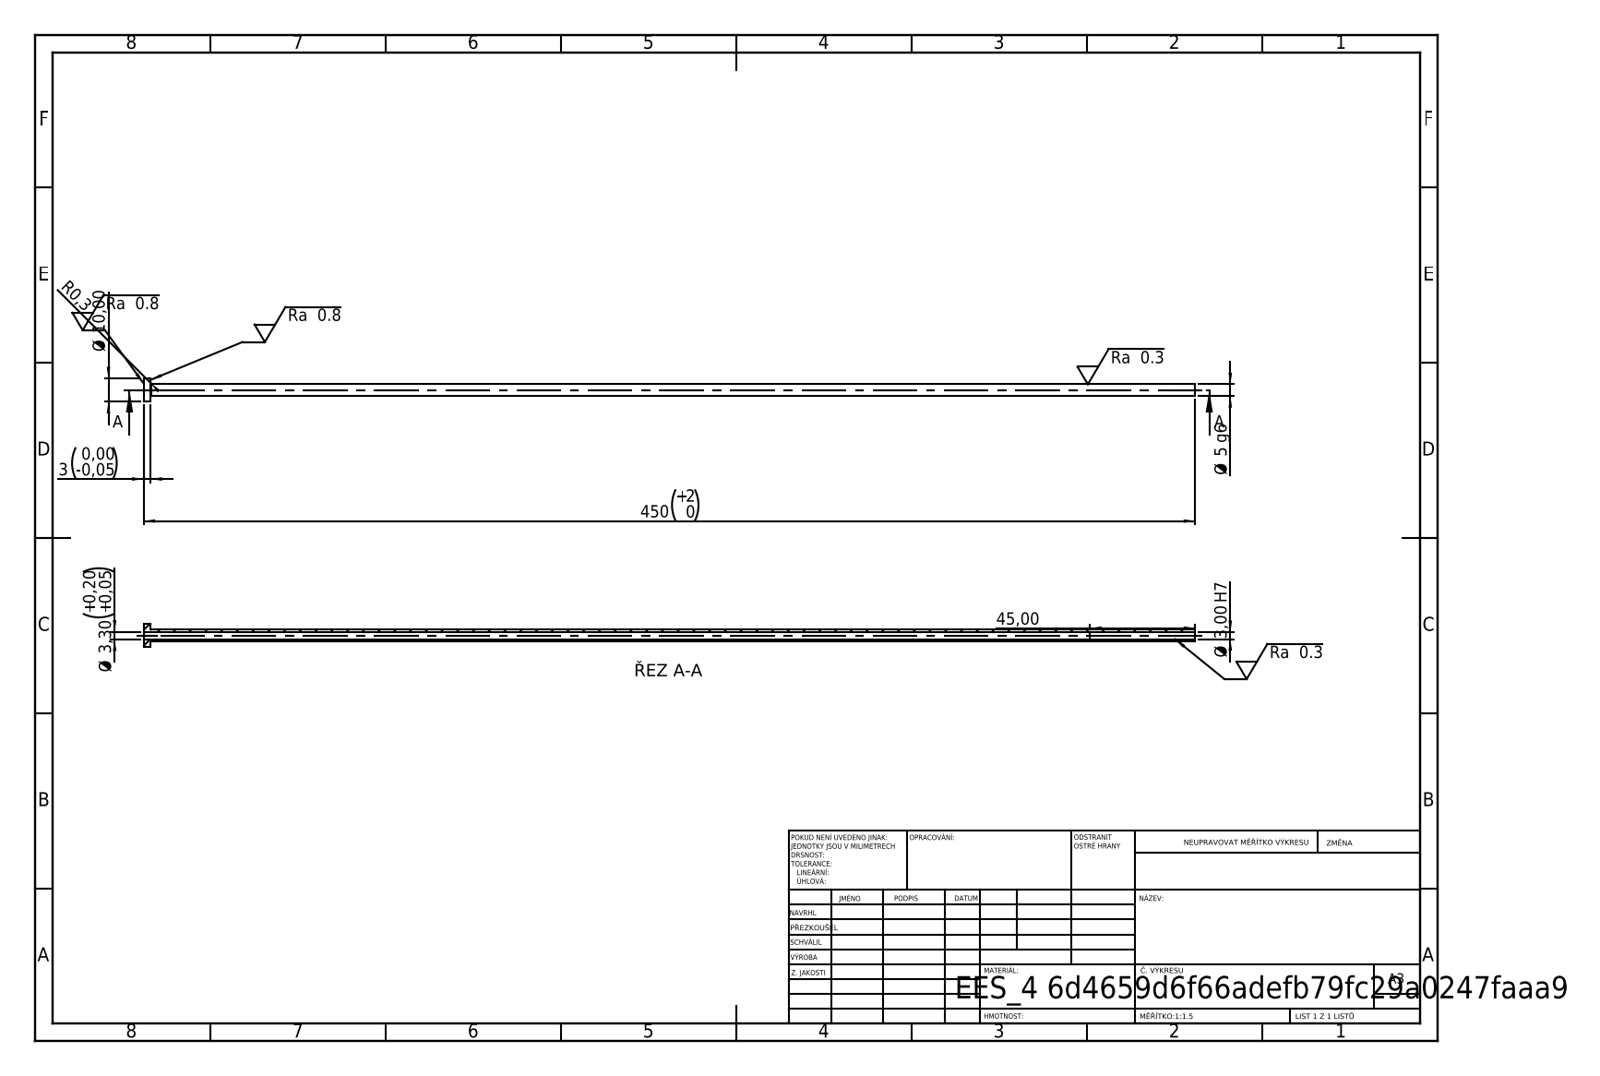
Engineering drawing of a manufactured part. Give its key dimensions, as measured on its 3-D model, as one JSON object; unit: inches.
{"step_written_by": "SolidWorks 2019 (CONFIG_CONTROL_DESIGN)", "units": "inches", "bodies": {"solids": 1, "faces": 14, "planar": 4, "cylindrical": 8, "other": 2}, "overall_size": [17.717, 0.394, 0.394], "volume_in3": 0.319, "surface_area_in2": 18.41, "round_holes": [[0.118, 1], [0.13, 1]], "round_bosses_or_shafts": [[0.394, 1], [0.197, 1]], "face_to_face_distances": [0.118, 17.717, 17.598, 15.945, 15.827, 1.772]}
